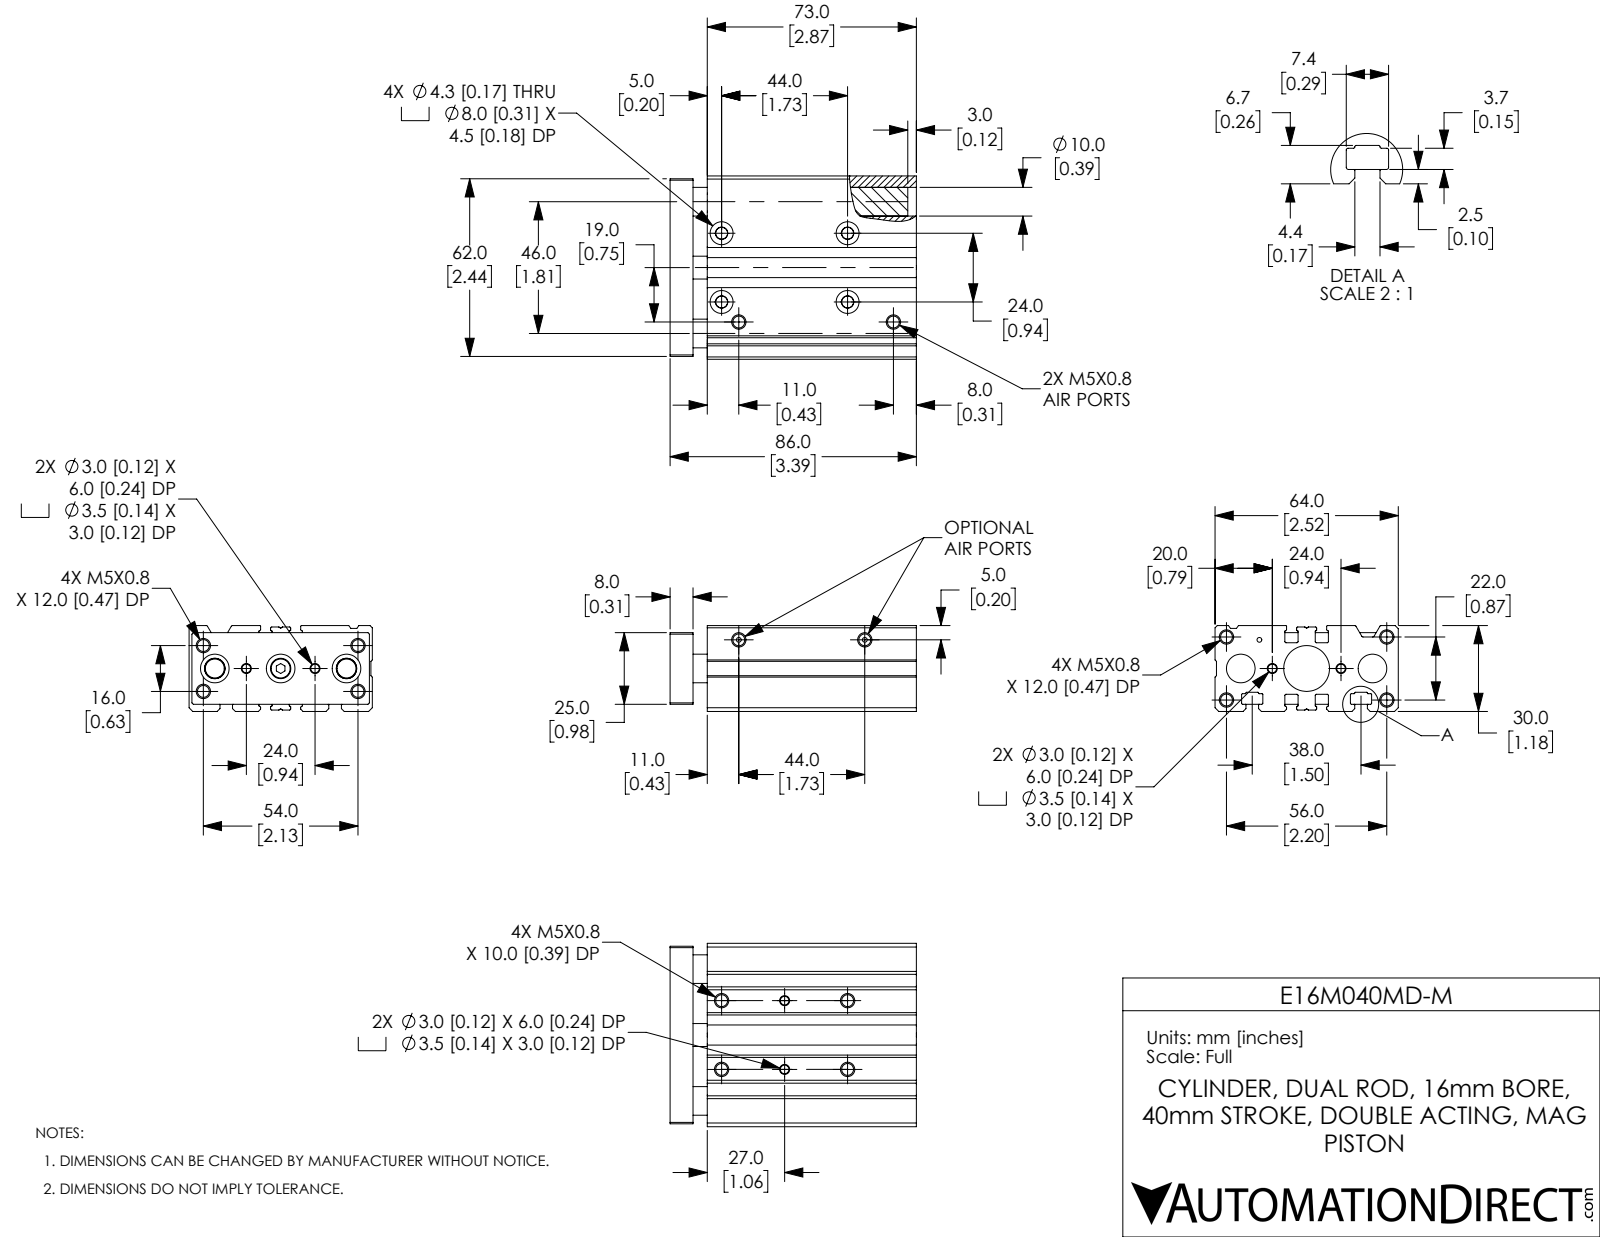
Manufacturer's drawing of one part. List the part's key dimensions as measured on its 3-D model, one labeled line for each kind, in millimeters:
Part name (STEP PRODUCT): E16M040MD-M_BODY; E16M040MD-M; E16M040MD-M_ENDPLATE
STEP written by: SolidWorks 2019 (CONFIG_CONTROL_DESIGN)
Units: millimetres
Bodies: 5 solids, 411 faces (133 planar, 192 cylindrical, 86 other)
Overall size (bounding box): 86 × 64 × 30
Volume: 125 620 mm³ · Surface area: 48 436 mm²
Round holes (diameter × count): ⌀4.13 ×16, ⌀3 ×4, ⌀3.5 ×4, ⌀4.3 ×4, ⌀8 ×4, ⌀1.67 ×3, ⌀5 ×3, ⌀10 ×3, ⌀7.11 ×2, ⌀10 ×1, ⌀16 ×1, ⌀16 ×1
Round bosses / shafts (diameter × count): ⌀8 ×1, ⌀7.11 ×1
Partial cylindrical surfaces — rounded edges, fillets, slot ends (radius × count): R0.2 ×22, R0.4 ×20, R0.25 ×8, R0.3 ×6, R0.5 ×4
Main face-to-face distances: 30, 0.5, 3.5, 6, 27.5, 29, 64, 78, 5, 4
Hole centre spacings: 22, 3.16, 8.94, 12.08, 17, 19.03, 19.42, 24
